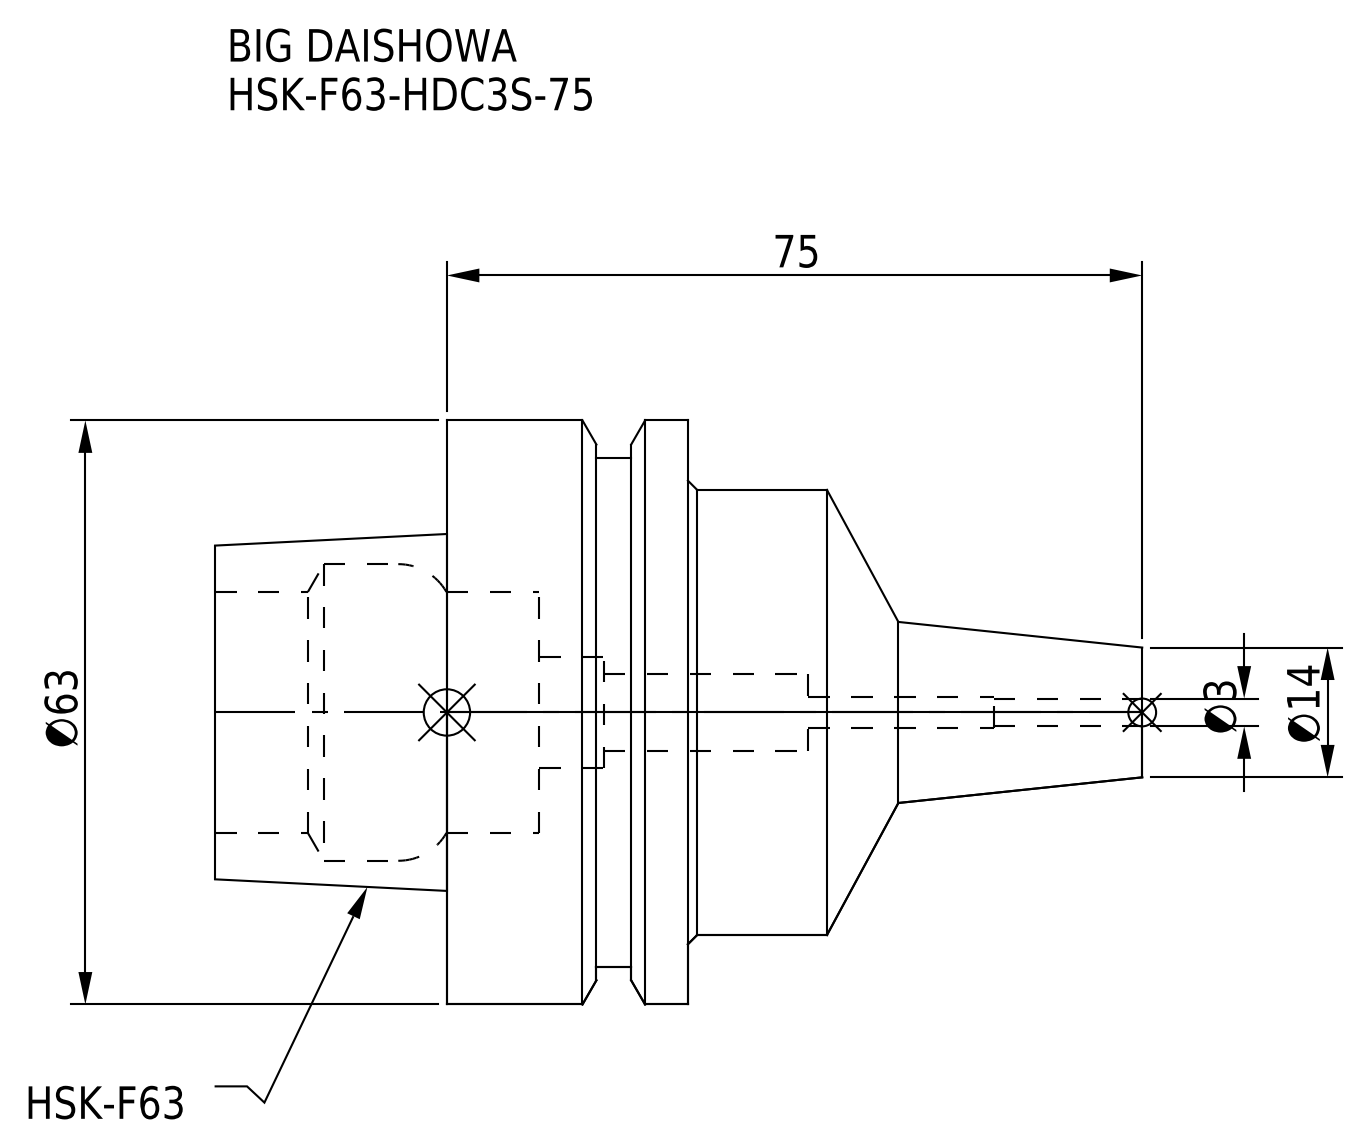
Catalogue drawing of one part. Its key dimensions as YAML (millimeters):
part_name: "HSK-F63-HDC3S-75"
step_written_by: "CREO PARAMETRIC BY PTC INC, 2016380 (AUTOMOTIVE_DESIGN)"
units: millimeters
bodies: {solids: 1, faces: 50, planar: 10, cylindrical: 24, other: 16}
overall_size: [100, 63, 63]
volume: 120930
surface_area: 23265
round_holes:
  - {diameter: 3, count: 1}
  - {diameter: 3.3, count: 1}
  - {diameter: 8.25, count: 1}
  - {diameter: 12, count: 1}
  - {diameter: 26, count: 1}
  - {diameter: 32, count: 1}
round_bosses_or_shafts:
  - {diameter: 63, count: 1}
  - {diameter: 55, count: 1}
  - {diameter: 48, count: 1}
face_to_face_distances: [26, 51, 25, 16.05, 9.95, 34.95, 6.12, 9.93, 19.88, 44.88]
